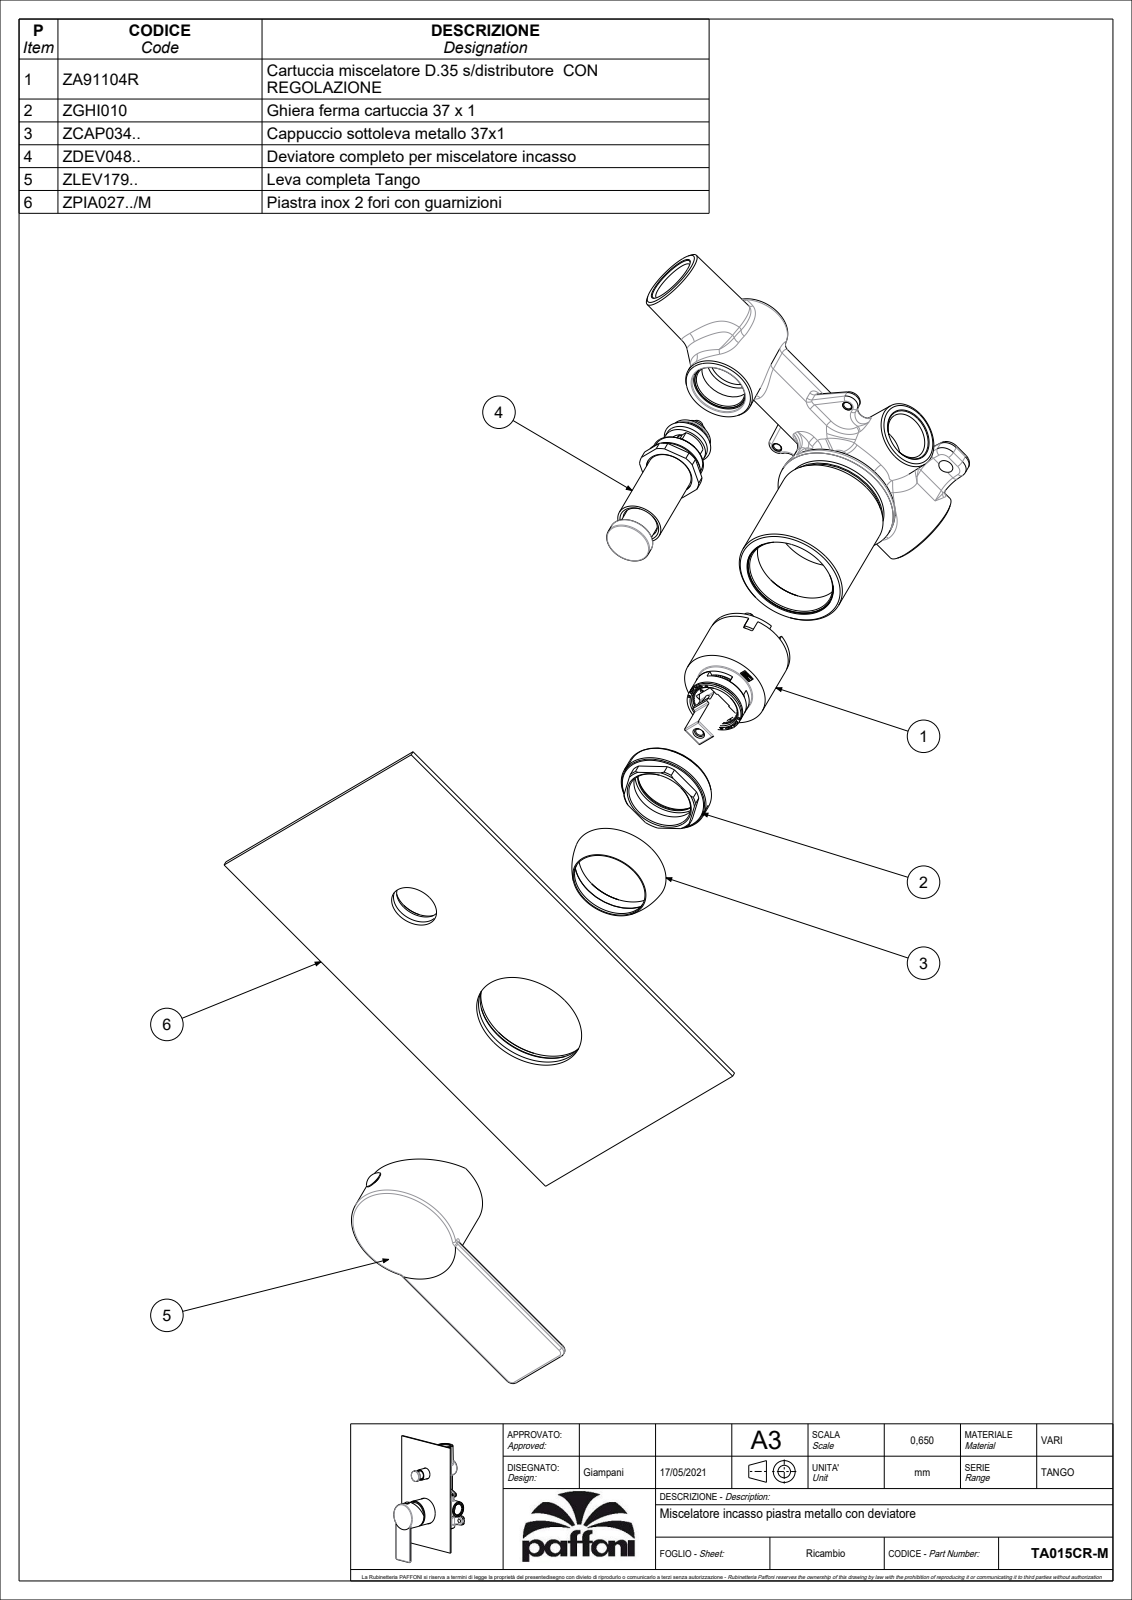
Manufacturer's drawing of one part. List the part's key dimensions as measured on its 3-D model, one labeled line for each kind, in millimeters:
Part name (STEP PRODUCT): TA015CR-M
STEP written by: CREO PARAMETRIC BY PTC INC, 2020044 (CONFIG_CONTROL_DESIGN)
Units: millimetres
Bodies: 3 solids, 180 faces (54 planar, 63 cylindrical, 63 other)
Overall size (bounding box): 205 × 120 × 59.8
Volume: 83 869 mm³ · Surface area: 75 366 mm²
Round holes (diameter × count): ⌀3 ×1, ⌀3.3 ×1, ⌀4.2 ×1, ⌀10.5 ×1, ⌀14.8 ×1, ⌀30.6 ×1, ⌀36 ×1, ⌀37.5 ×1
Round bosses / shafts (diameter × count): ⌀45.5 ×1, ⌀44.8 ×1, ⌀18.7 ×1, ⌀18.6 ×1, ⌀14 ×1, ⌀7.6 ×1, ⌀5.5 ×1
Partial cylindrical surfaces — rounded edges, fillets, slot ends (radius × count): R1 ×6, R1.5 ×4, R0.5 ×2, R3 ×2, R3.5 ×1
Main face-to-face distances: 2, 54.3, 59.3, 57.3, 3, 56.3, 3.5, 0.5, 55.8, 53.8
Hole centre spacings: 68
